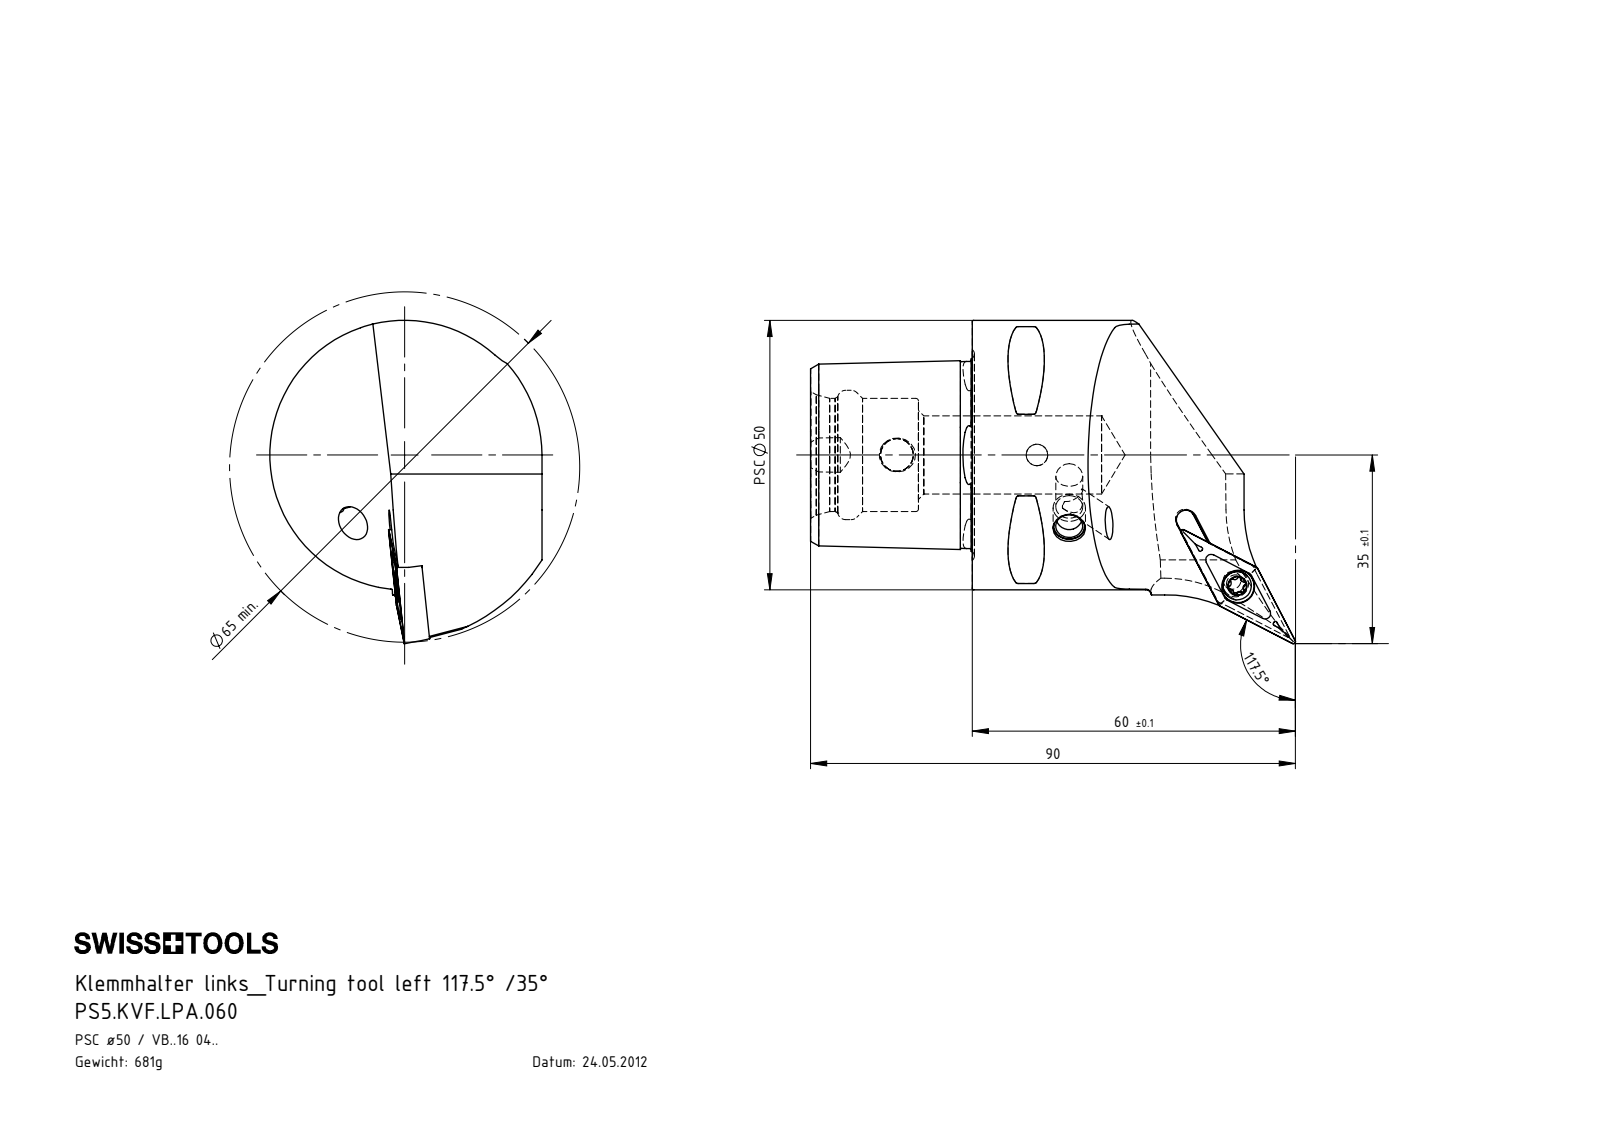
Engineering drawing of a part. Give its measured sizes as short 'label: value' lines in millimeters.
name: VBMT160404; PS5.KVF.LPA.060; KVT_MB_600_060; WCB-ER2.001.009_A (+1 more)
written by: SolidWorks 2017 (AUTOMOTIVE_DESIGN)
unit: mm
bodies: 5 solids, 206 faces (56 planar, 48 cylindrical, 102 other)
size: 90 × 60 × 50.5
volume: 86 211 mm³; area: 18 892 mm²
holes: 3× ⌀5, 2× ⌀6.1, 1× ⌀3.3, 1× ⌀4, 1× ⌀4.4, 1× ⌀6, 1× ⌀14.5, 1× ⌀21, 1× ⌀24
bosses: 1× ⌀50, 1× ⌀6, 1× ⌀5.25, 1× ⌀4
rounds: 8× R0.5, 6× R0.34, 6× R0.59, 2× R0.15, 2× R26, 1× R1.75, 1× R3, 1× R4
face distances: 30, 19.18, 44.4, 4.43, 4.44, 20, 10, 29.8, 9.8, 4.76
hole spacings: 26
